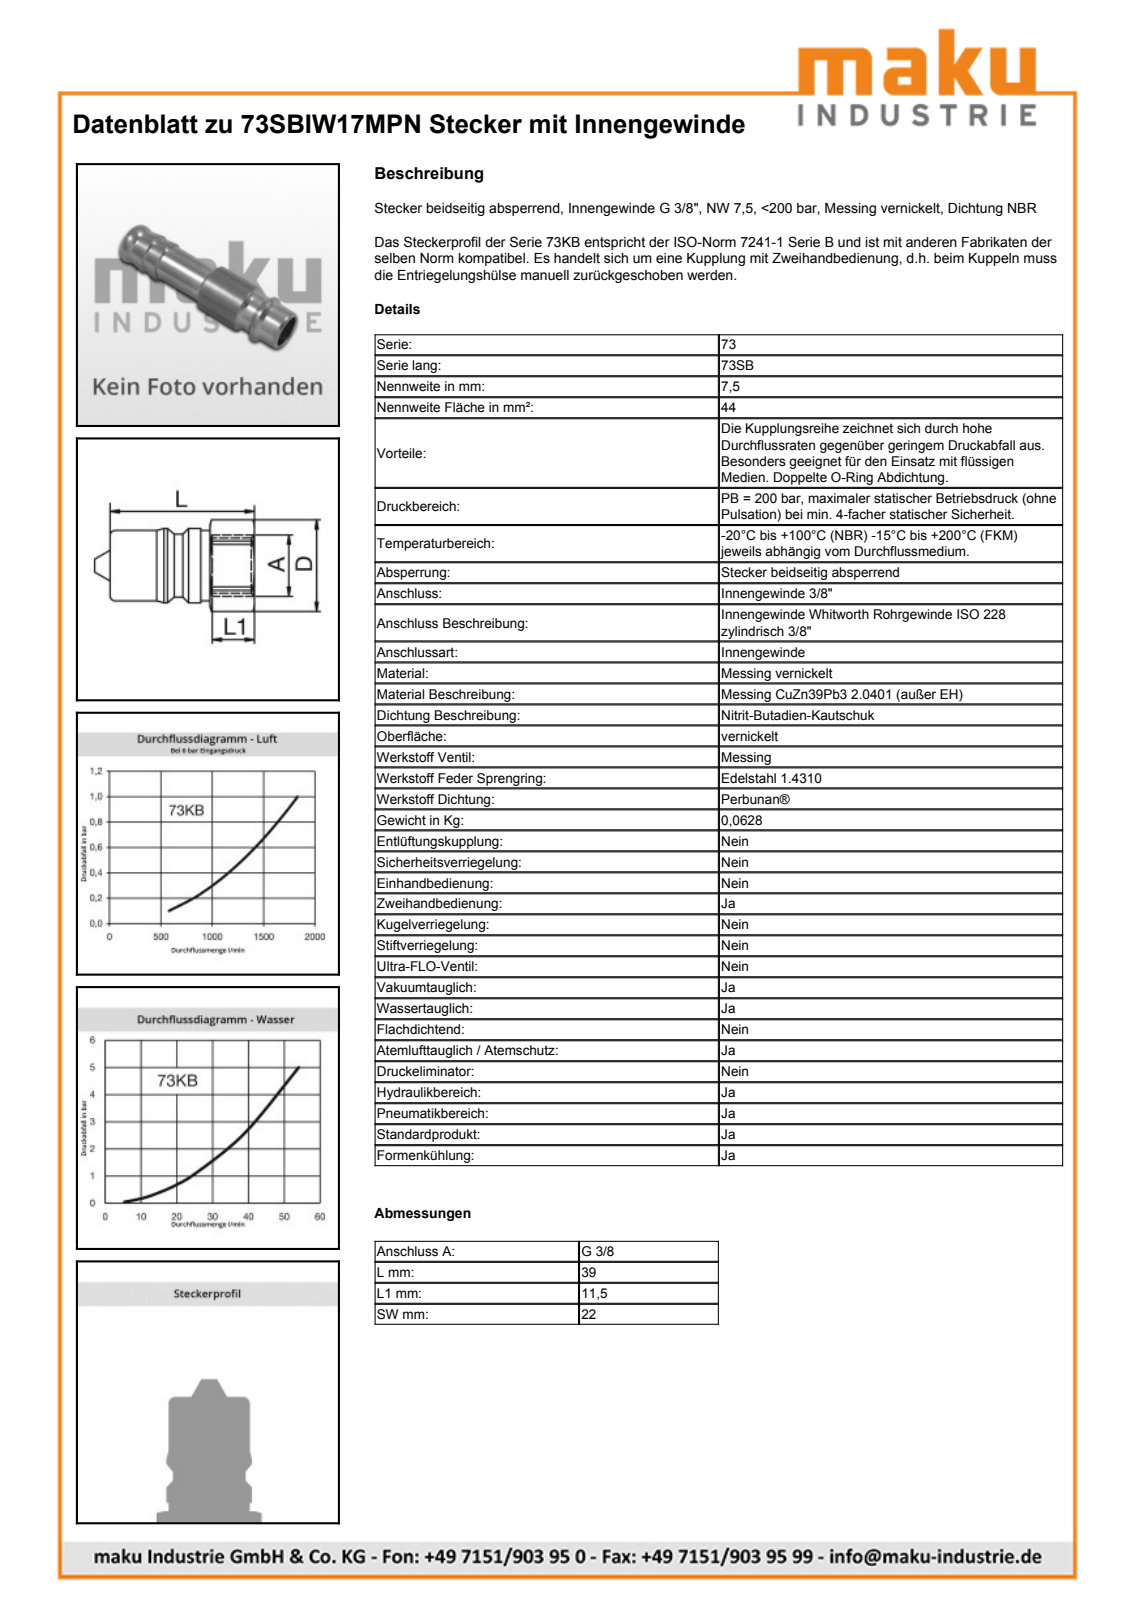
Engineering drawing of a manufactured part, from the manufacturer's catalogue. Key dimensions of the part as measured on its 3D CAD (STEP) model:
Part name (STEP PRODUCT): D108977
STEP written by: Autodesk Inventor 2013 (AUTOMOTIVE_DESIGN)
Units: millimetres
Bodies: 1 solid, 53 faces (15 planar, 15 cylindrical, 23 other)
Overall size (bounding box): 43.57 × 24.8 × 22
Volume: 9 645 mm³ · Surface area: 4 169 mm²
Round holes (diameter × count): ⌀14.15 ×1, ⌀16.66 ×1
Round bosses / shafts (diameter × count): ⌀20.09 ×1, ⌀19.05 ×1, ⌀19 ×1, ⌀17 ×1, ⌀16.73 ×1, ⌀3 ×1
Partial cylindrical surfaces — rounded edges, fillets, slot ends (radius × count): R12.4 ×1
Main face-to-face distances: 22, 24.79, 39, 14.21, 27, 2.21, 12, 24.8, 2.2, 14.2
